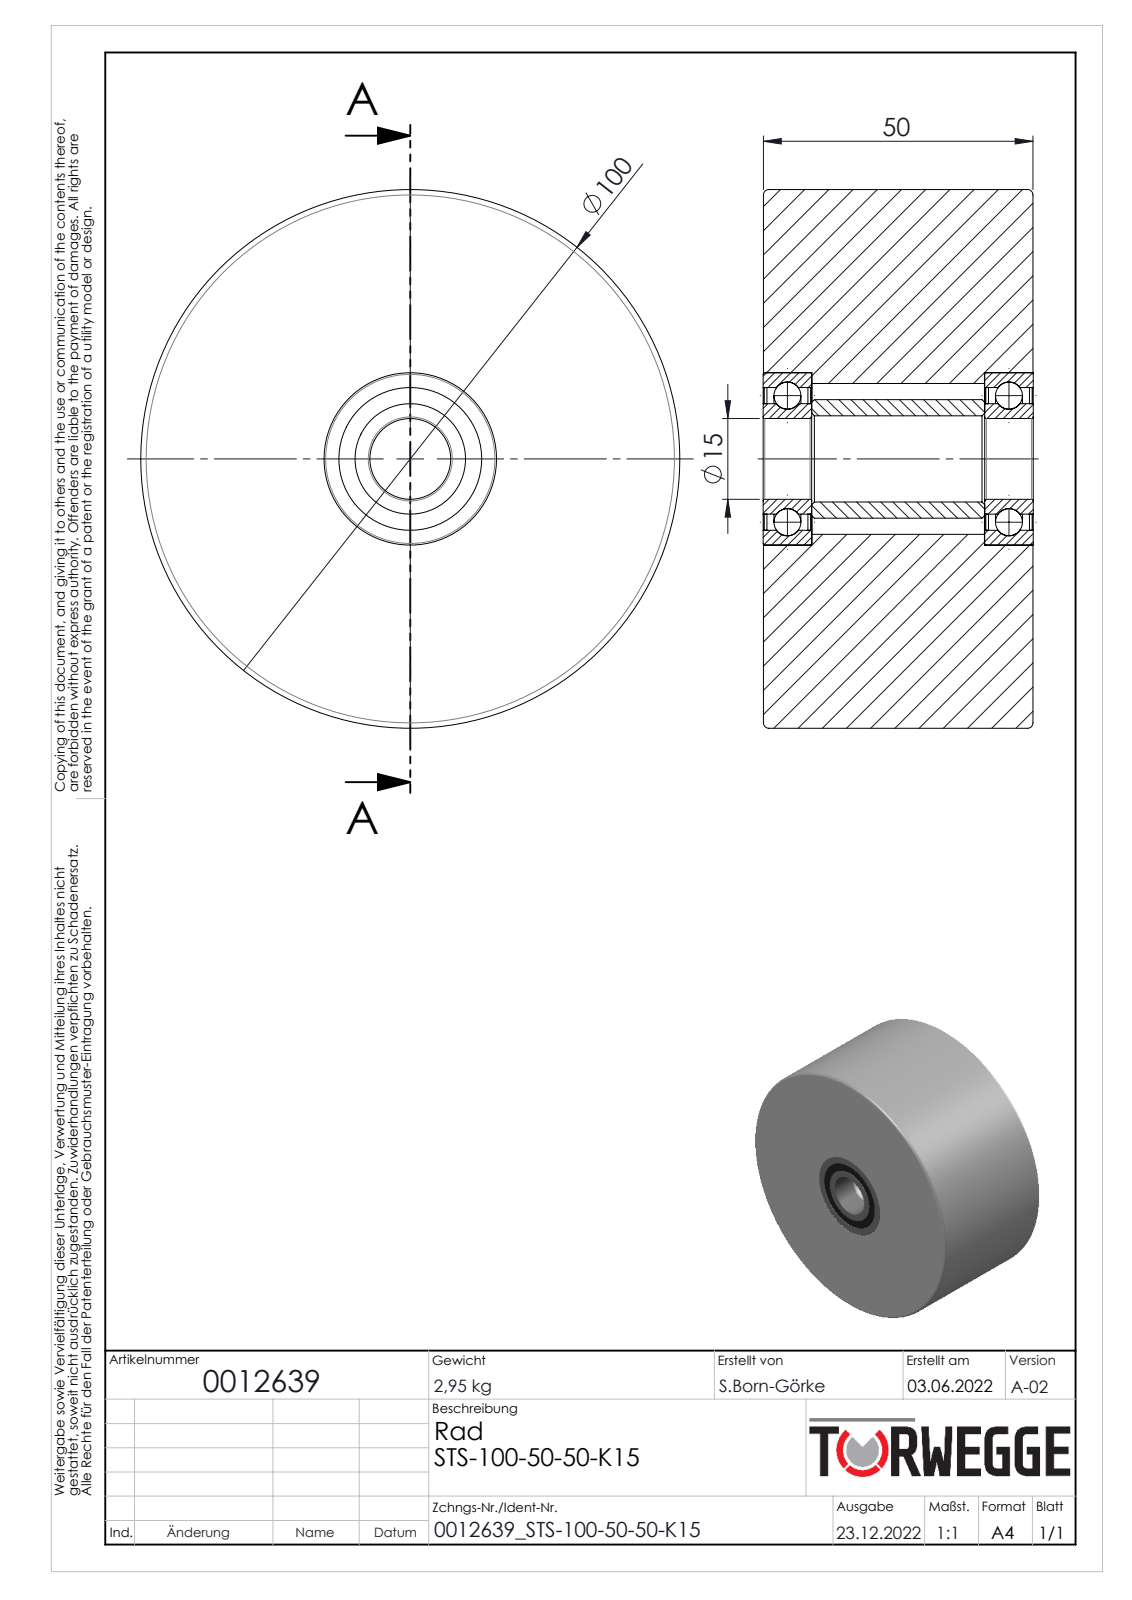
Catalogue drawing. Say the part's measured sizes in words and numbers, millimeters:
The part is named "0012639". Its 3-D file was written by "SolidWorks 2020 (AUTOMOTIVE_DESIGN)". It is 12 solids with 122 faces: 22 planar, 52 cylindrical and 48 other. Overall it measures 100 by 100 by 50.1 millimeters. Its volume is 373 847 cubic millimeters and its surface area 50 110 square millimeters. Round holes: 1 of diameter 15, 1 of diameter 16, 1 of diameter 20.5, 1 of diameter 26.5, 1 of diameter 28, 1 of diameter 32. Round bosses or shafts: 1 of diameter 100, 1 of diameter 22. The main face-to-face distances are 50, 41.1, 41.05, 9, 8.95, 0.7, 8.3, 8.8, 0.5, 8.1.
